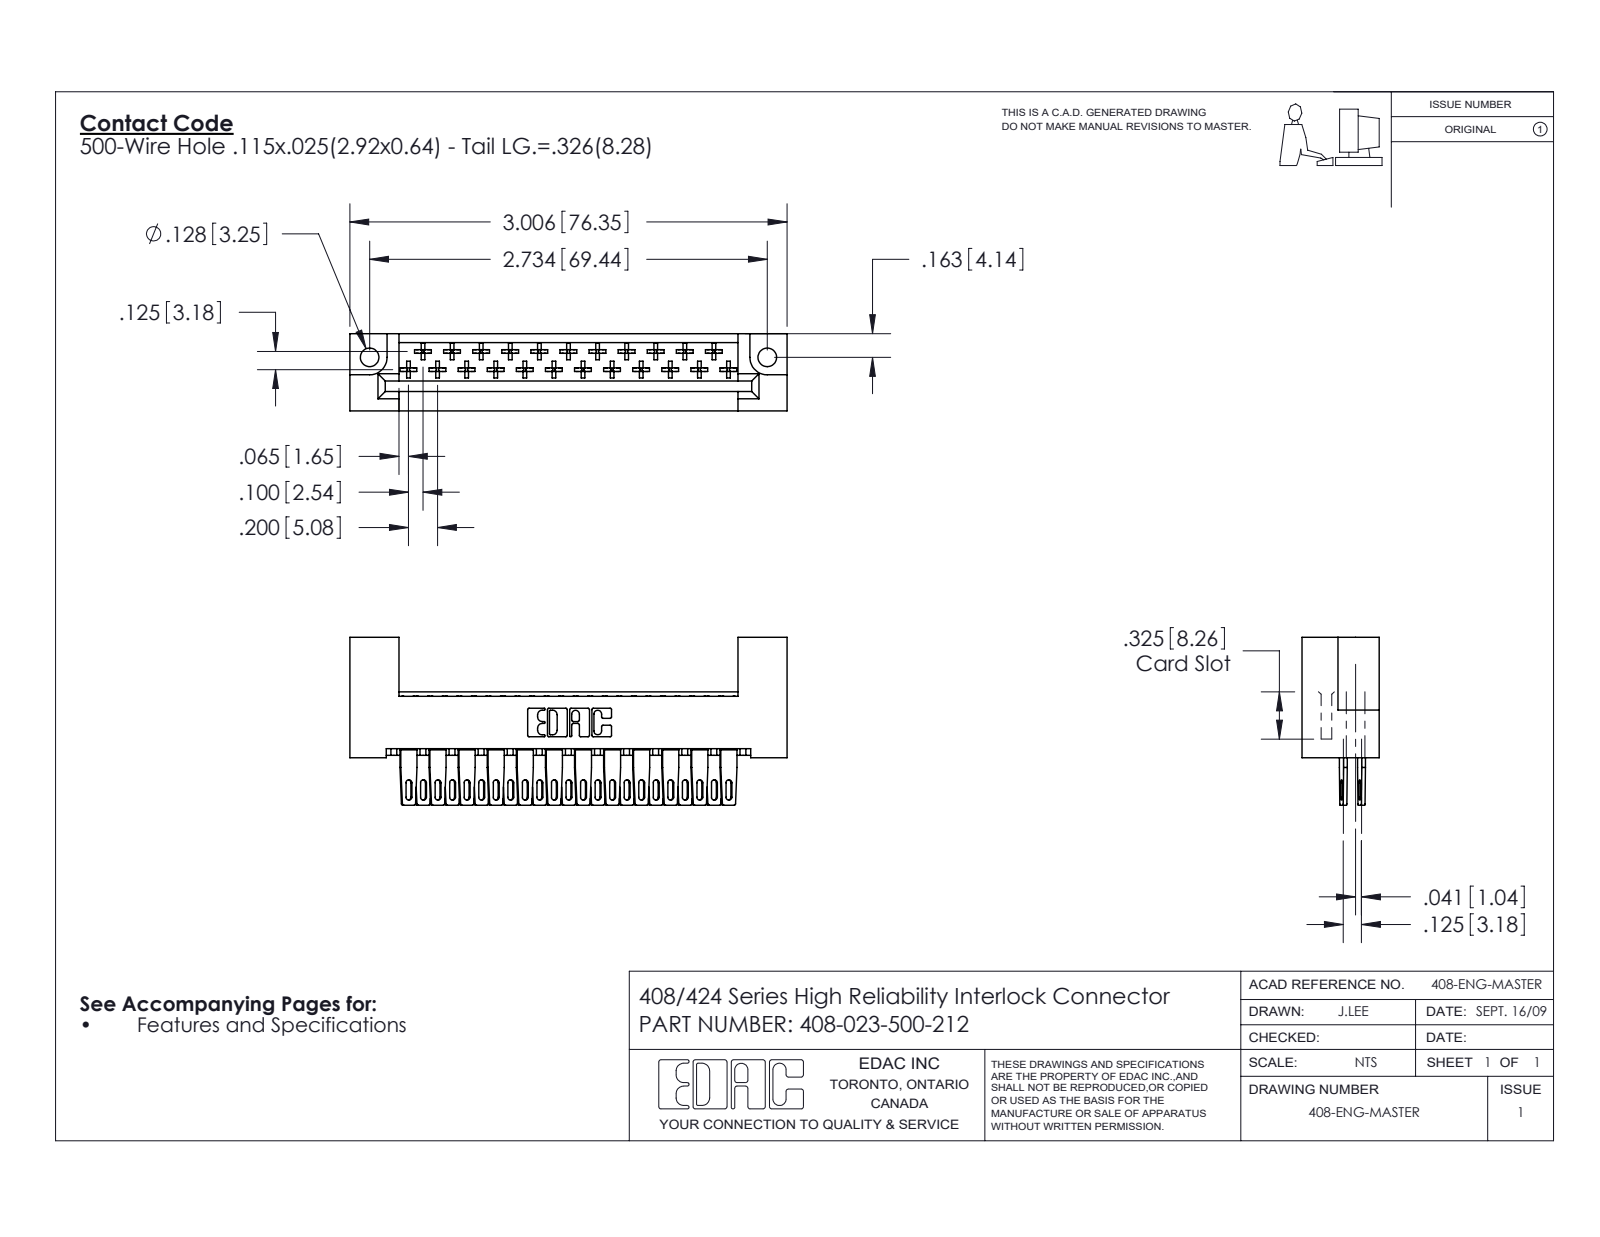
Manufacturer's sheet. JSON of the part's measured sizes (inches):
{"part_name": "408 Part_023 - 2; 408-023-500-212; 408-290-001_408-290-100", "step_written_by": "SolidWorks 2016 (CONFIG_CONTROL_DESIGN)", "units": "inches", "bodies": {"solids": 24, "faces": 1450, "planar": 1032, "cylindrical": 326, "other": 92}, "overall_size": [3.006, 1.154, 0.531], "volume_in3": 0.619, "surface_area_in2": 18.36, "round_holes": [[0.128, 2]], "partial_cylinders_radius": [[0.01, 184], [0.021, 46], [0.02, 25], [0.01, 22], [0.007, 6], [0.031, 6], [0.026, 3], [0.12, 2]], "face_to_face_distances": [0.531, 0.125, 0.1, 0.025, 0.025, 0.361, 0.326, 0.235, 0.259, 0.205], "hole_center_spacings": [2.734]}
